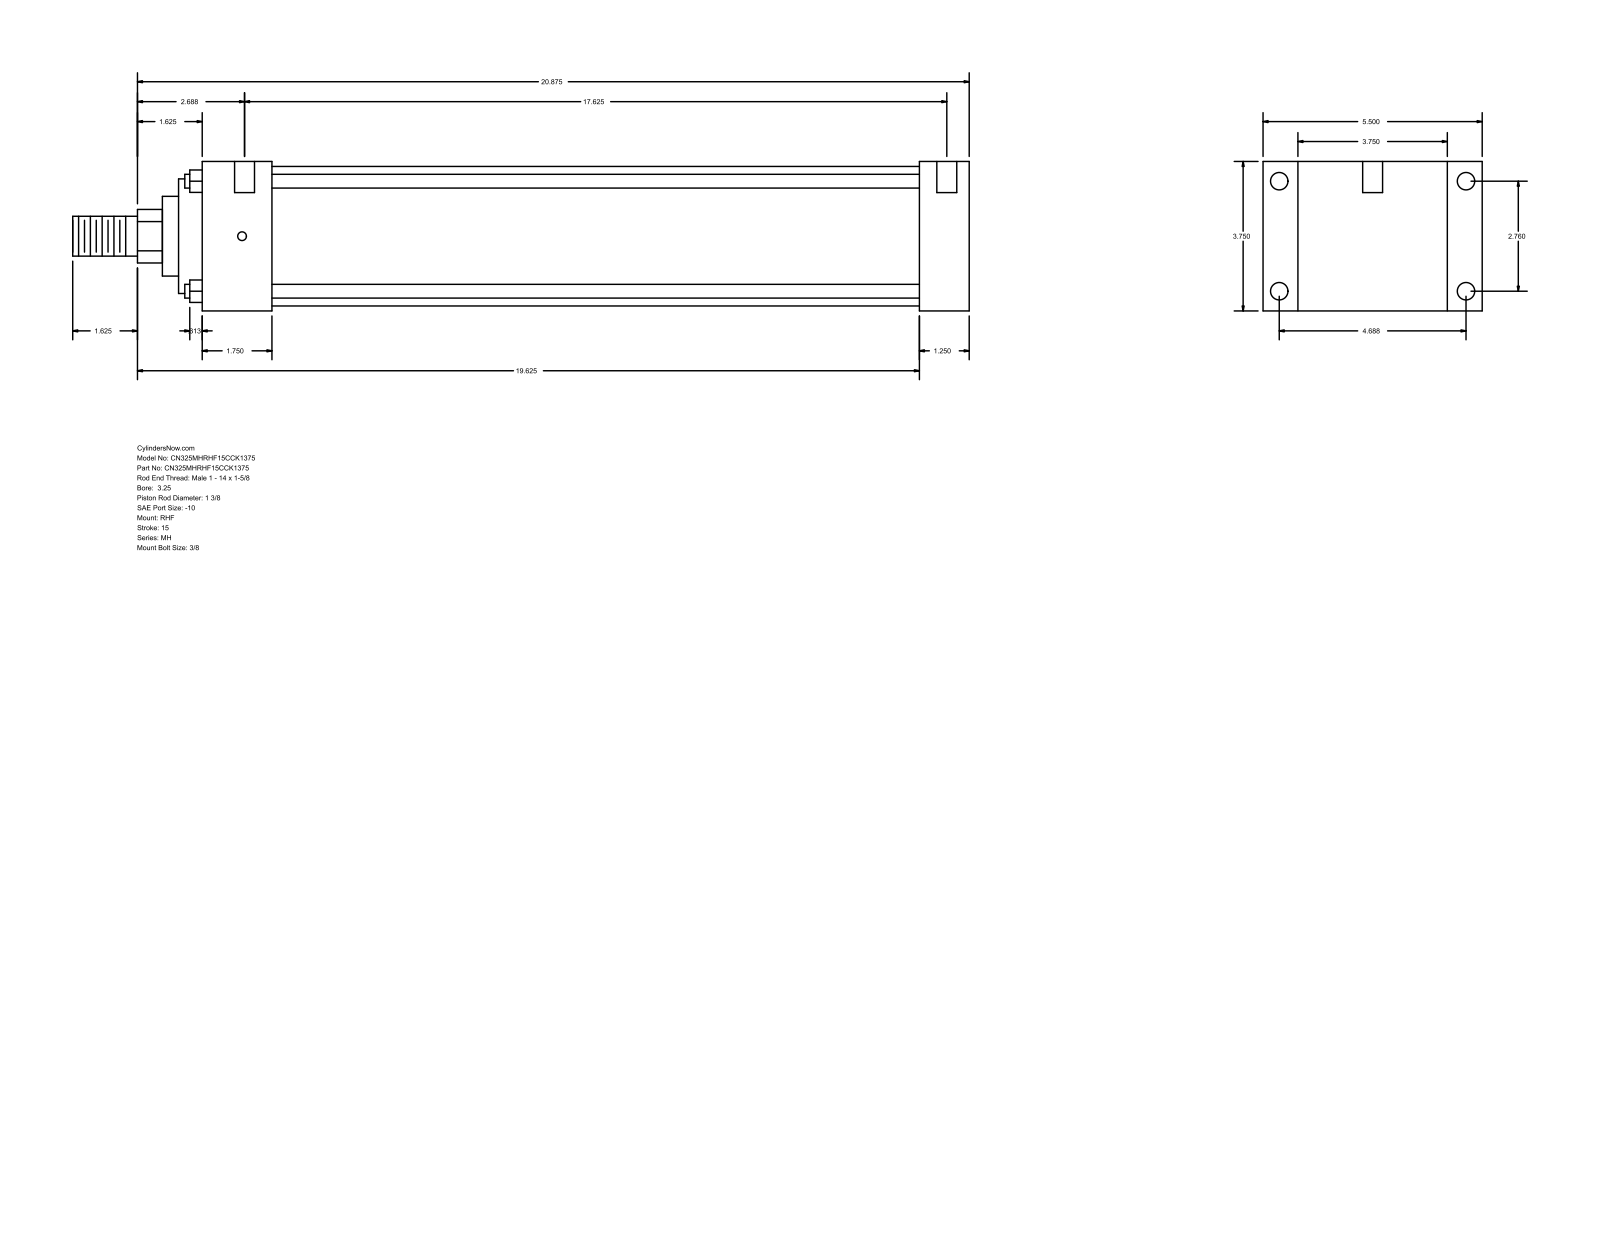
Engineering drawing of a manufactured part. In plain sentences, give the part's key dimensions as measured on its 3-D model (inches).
The part is named "MH_RHF__0325_1.375". Its 3-D file was written by "GSSL Pune (CONFIG_CONTROL_DESIGN)". It is 0 solids with 90 faces: 61 planar, 29 cylindrical and 0 other. Overall it measures 22.5 by 5.5 by 3.75 inches. Round holes: 4 of diameter 0.219, 4 of diameter 0.438, 2 of diameter 0.5. Round bosses or shafts: 4 of diameter 0.345, 1 of diameter 3.5, 1 of diameter 2.875, 1 of diameter 2, 1 of diameter 1.375, 1 of diameter 1. Partial cylindrical surfaces (rounded edges, fillets, slot ends): 1 of radius 0.672. The main face-to-face distances are 3.75, 1.25, 0.875, 4.625, 18, 19.25, 5.5, 1.75, 16.25, 17.5. The hole center spacings are 2.76, 4.687, 5.439, 17.875, 0.063, 0.187, 17.625, 17.688.
